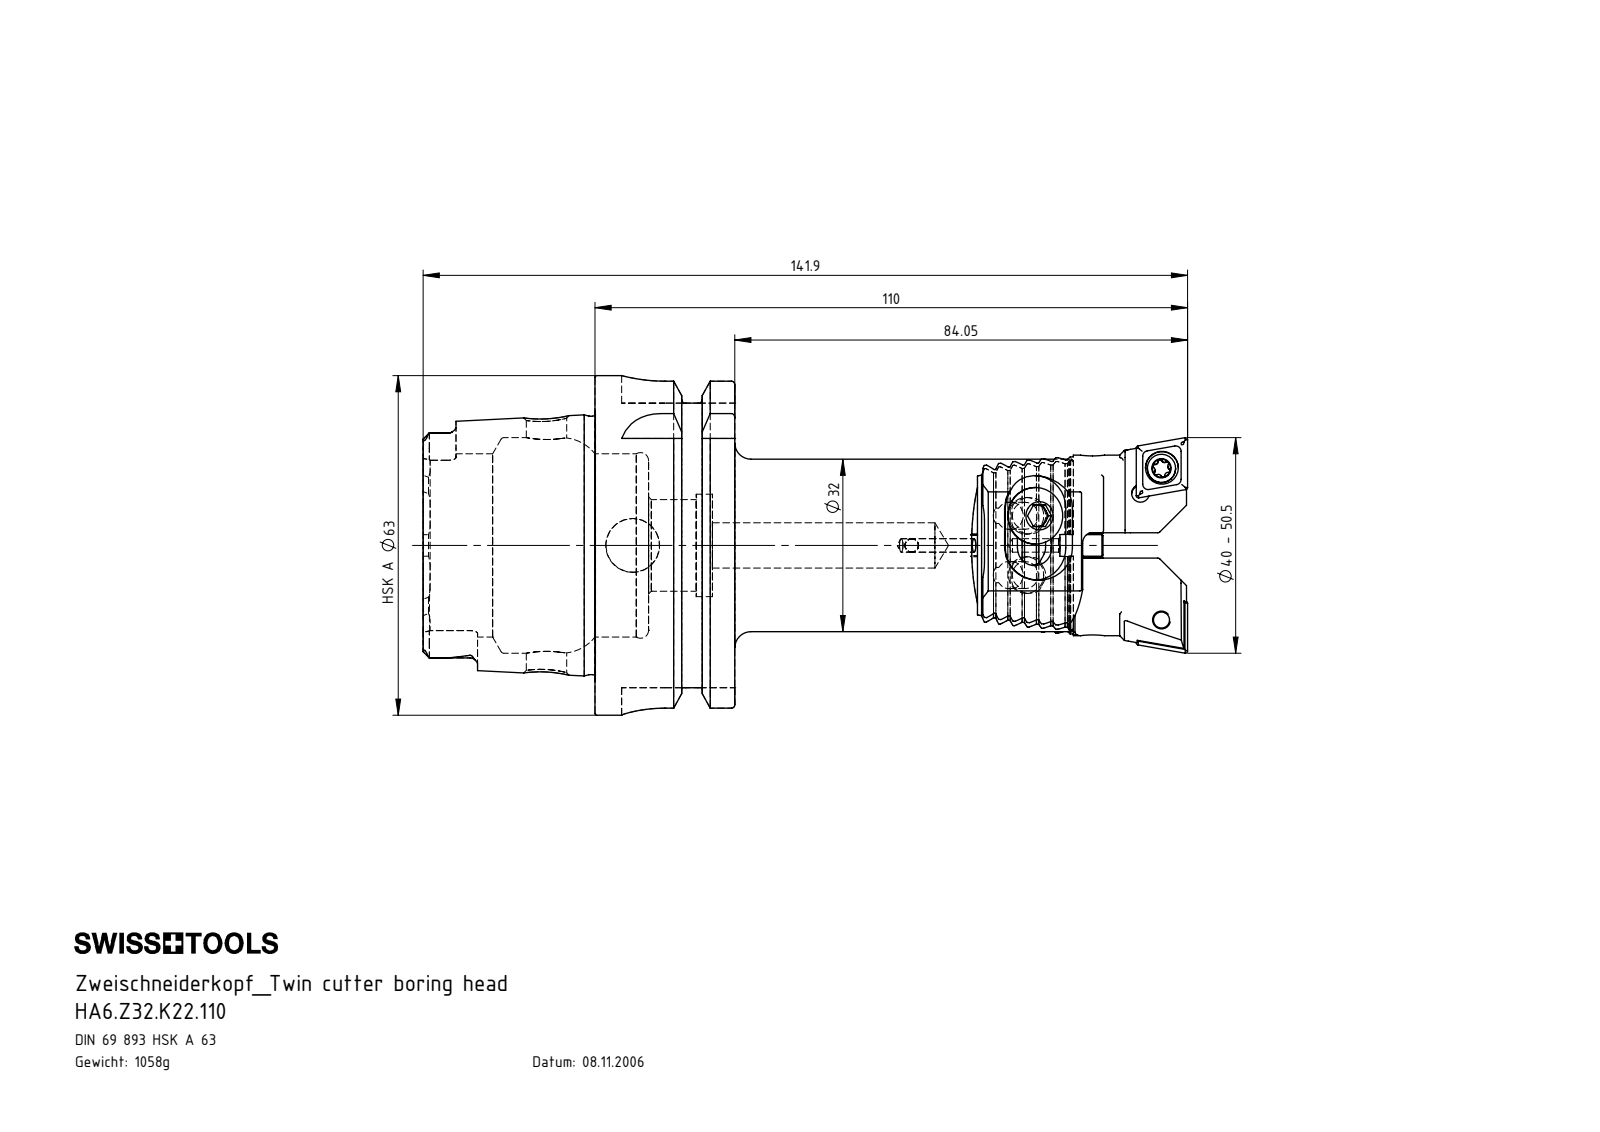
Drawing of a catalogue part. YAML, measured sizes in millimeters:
part_name: "WCB-ER2.001.009_A; Z32-WCB.001.021; Z32-ER3.001.013_A; Z32-xxx.001.021_B (+6 more)"
step_written_by: "SolidWorks 2022 (CONFIG_CONTROL_DESIGN)"
units: millimeters
bodies: {solids: 12, faces: 893, planar: 360, cylindrical: 252, other: 281}
overall_size: [141.9, 63, 63]
volume: 134693
surface_area: 39838
round_holes:
  - {diameter: 2.5, count: 4}
  - {diameter: 3.3, count: 4}
  - {diameter: 1.6, count: 2}
  - {diameter: 2, count: 2}
  - {diameter: 4.4, count: 2}
  - {diameter: 5, count: 2}
  - {diameter: 6.1, count: 2}
  - {diameter: 6.8, count: 2}
  - {diameter: 3.5, count: 1}
  - {diameter: 7.5, count: 1}
  - {diameter: 8.4, count: 1}
  - {diameter: 10, count: 1}
round_bosses_or_shafts:
  - {diameter: 4, count: 4}
  - {diameter: 10.5, count: 2}
  - {diameter: 6, count: 2}
  - {diameter: 5.25, count: 2}
  - {diameter: 63, count: 1}
  - {diameter: 54.95, count: 1}
  - {diameter: 47.94, count: 1}
  - {diameter: 32, count: 1}
partial_cylinders:
  - {radius: 0.5, count: 16}
  - {radius: 0.2, count: 14}
  - {radius: 0.2, count: 12}
  - {radius: 0.34, count: 12}
  - {radius: 0.59, count: 12}
  - {radius: 1.4, count: 6}
  - {radius: 2, count: 4}
  - {radius: 2.88, count: 4}
face_to_face_distances: [2.38, 25.95, 4.76, 16, 9.53, 7.15, 2.42, 2.34, 7.14, 9.95]
hole_center_spacings: [6.07, 6.19, 9, 24.23, 24.33, 28.65, 104.04, 17.38]
